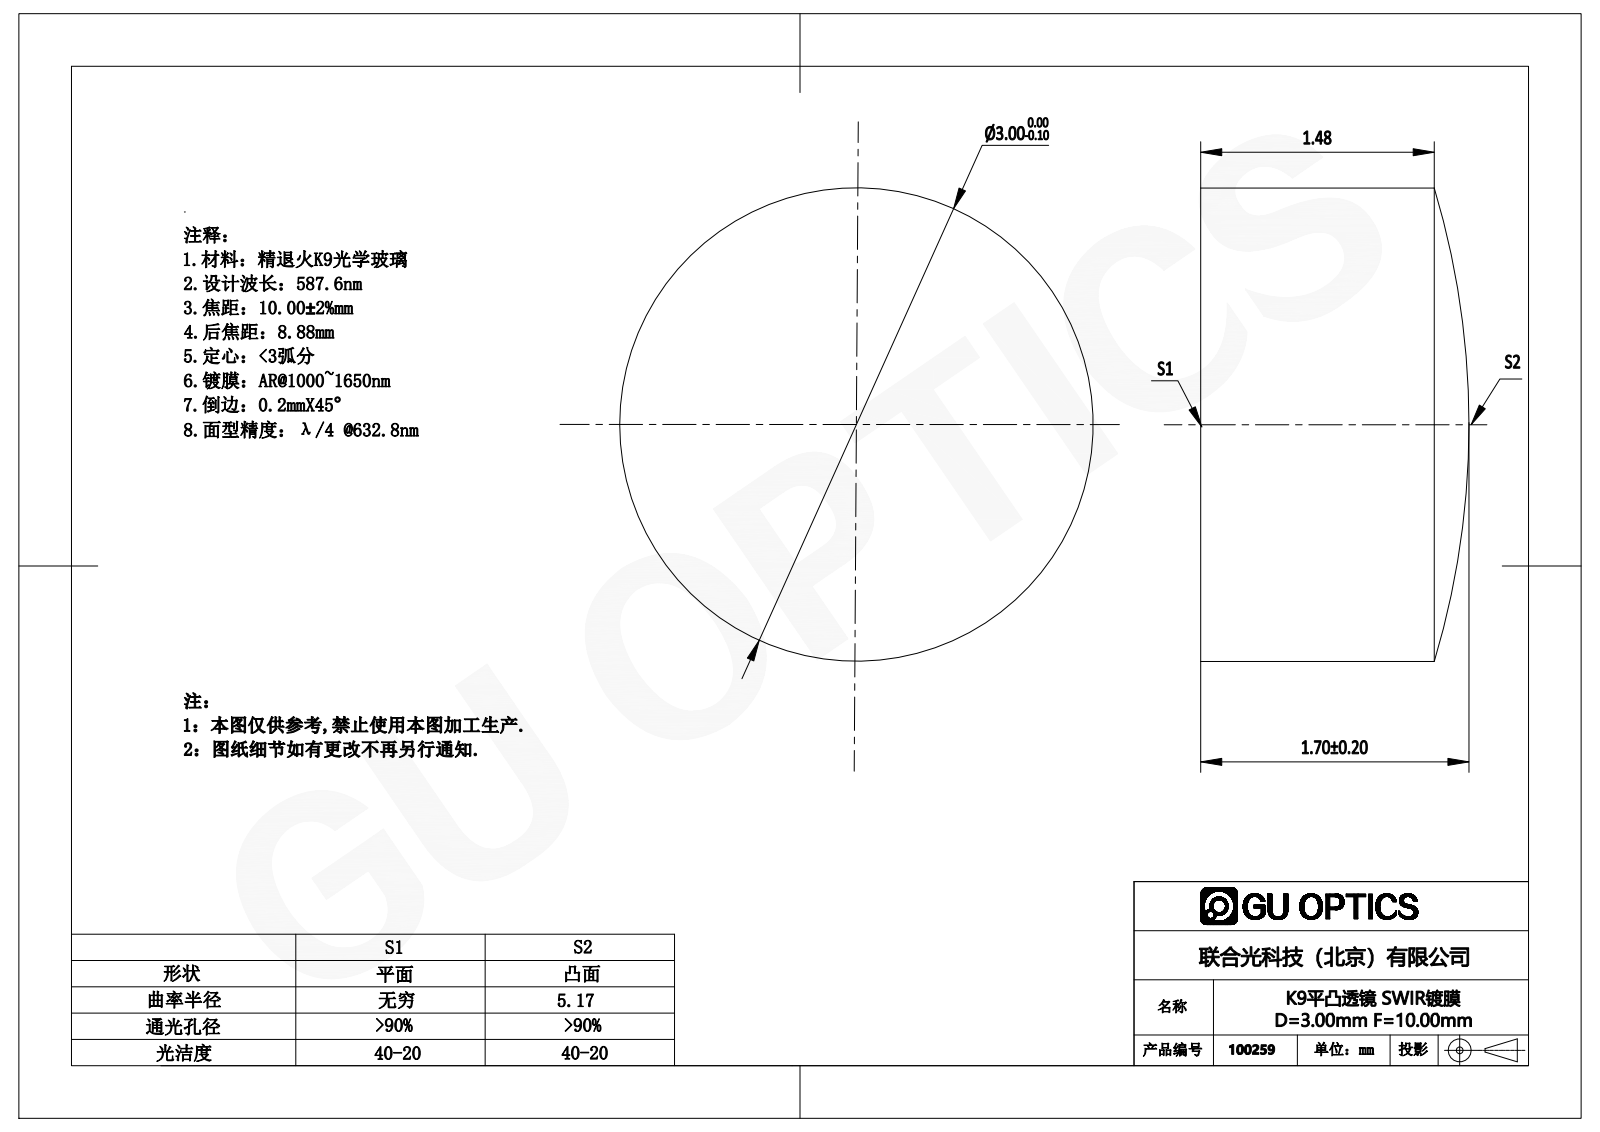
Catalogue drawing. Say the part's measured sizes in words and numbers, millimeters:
The part is named "100087". Its 3-D file was written by "SolidWorks 2016 (AUTOMOTIVE_DESIGN)". It is 1 solid with 5 faces: 1 planar, 2 cylindrical and 2 other. Overall it measures 3 by 3 by 1.7 millimeters. Its volume is 11 cubic millimeters and its surface area 28 square millimeters. Round bosses or shafts: 1 of diameter 3.
